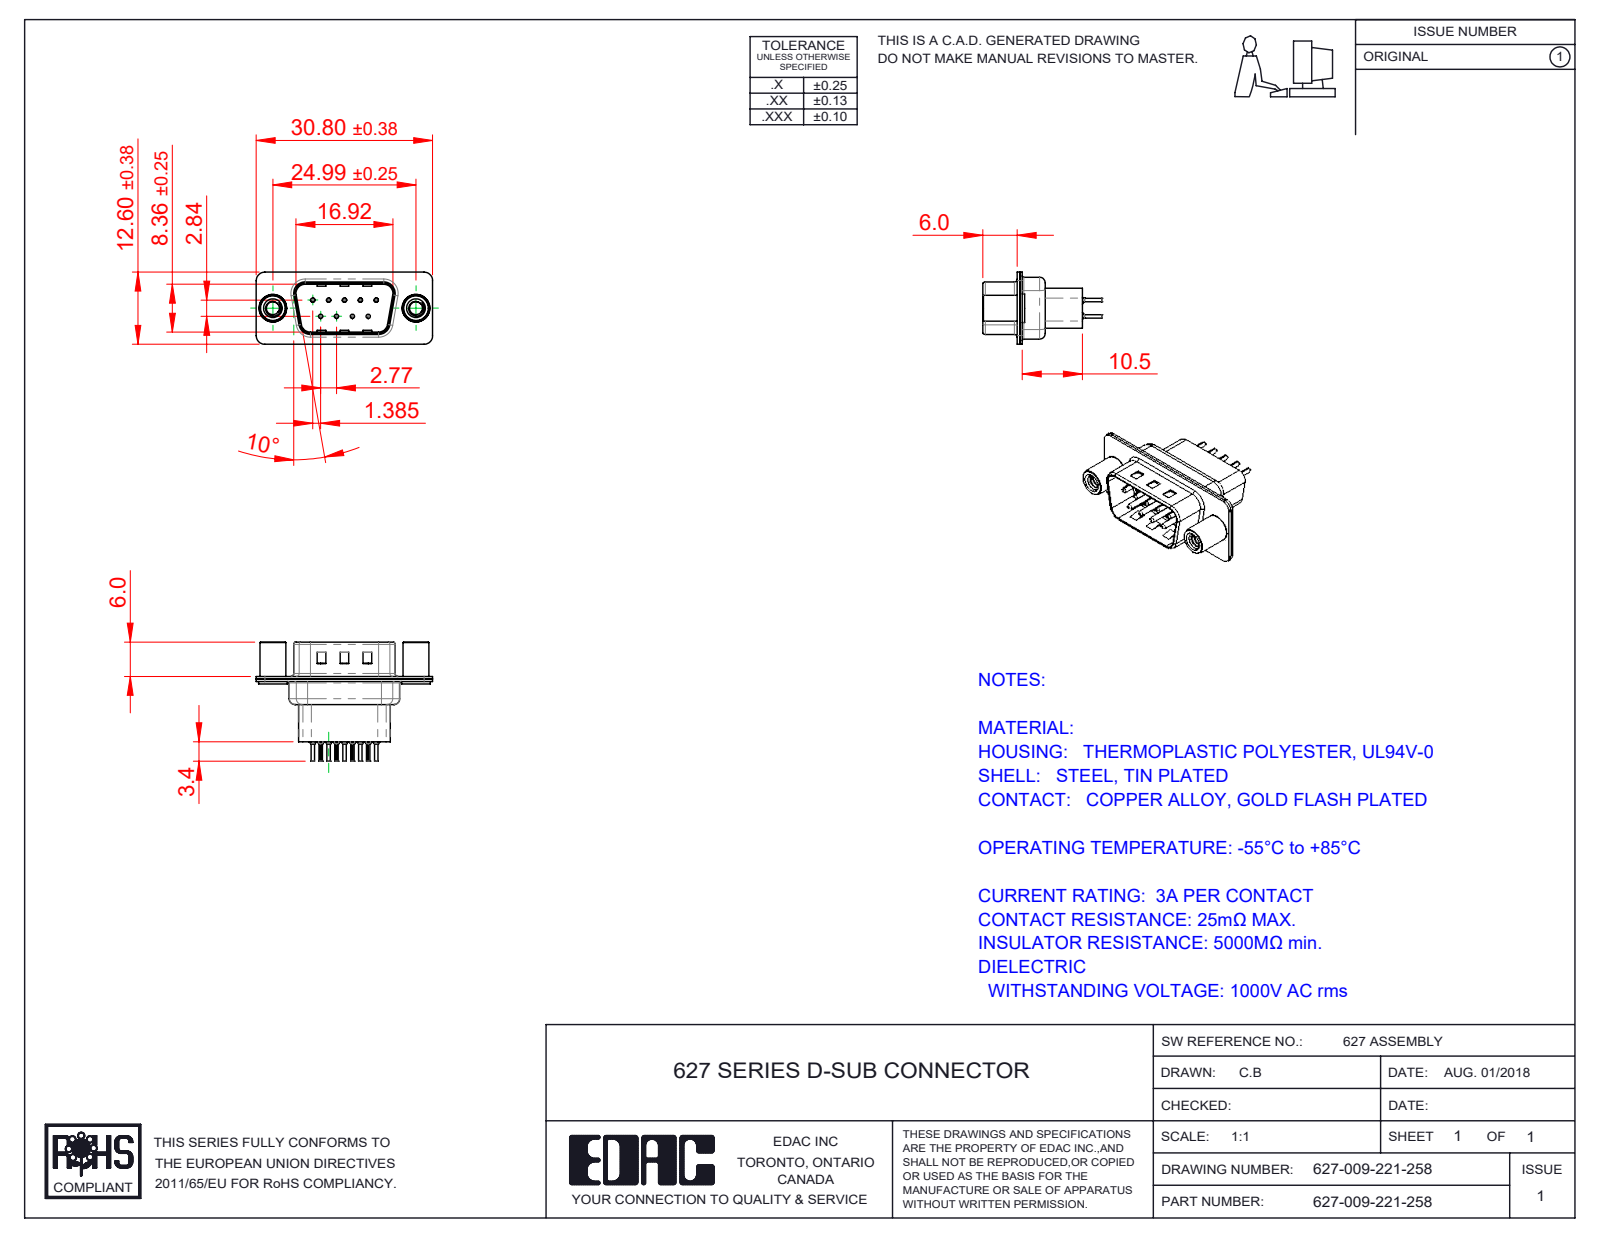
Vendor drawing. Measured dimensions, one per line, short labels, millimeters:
name: 627 Contact Row 2_21H; 627-009-221-058; 627 Shell Front_09 Contacts; 627 Housing_09 HP (+3 more)
written by: SolidWorks 2020 (CONFIG_CONTROL_DESIGN)
unit: mm
bodies: 14 solids, 1220 faces (325 planar, 490 cylindrical, 405 other)
size: 30.8 × 20.8 × 12.6
volume: 1 835 mm³; area: 4 894 mm²
holes: 9× ⌀0.2, 9× ⌀0.35, 9× ⌀1.1, 9× ⌀1.6, 2× ⌀2.26, 2× ⌀4, 2× ⌀4.8
bosses: 9× ⌀2, 9× ⌀1.5, 9× ⌀0.75, 9× ⌀0.6, 2× ⌀5, 2× ⌀4.9, 2× ⌀4.5
rounds: 18× R0.1, 18× R1.5, 12× R2, 8× R0.5, 8× R1.6, 4× R0.25, 4× R0.6, 4× R0.65
face distances: 0.4, 0.45, 0.9, 0.82, 9.58, 1.4, 1.5, 0.68, 7.68, 1.08
hole spacings: 3.16, 2.77, 5.54, 5.03, 5.04, 8.31, 7.48, 7.49
